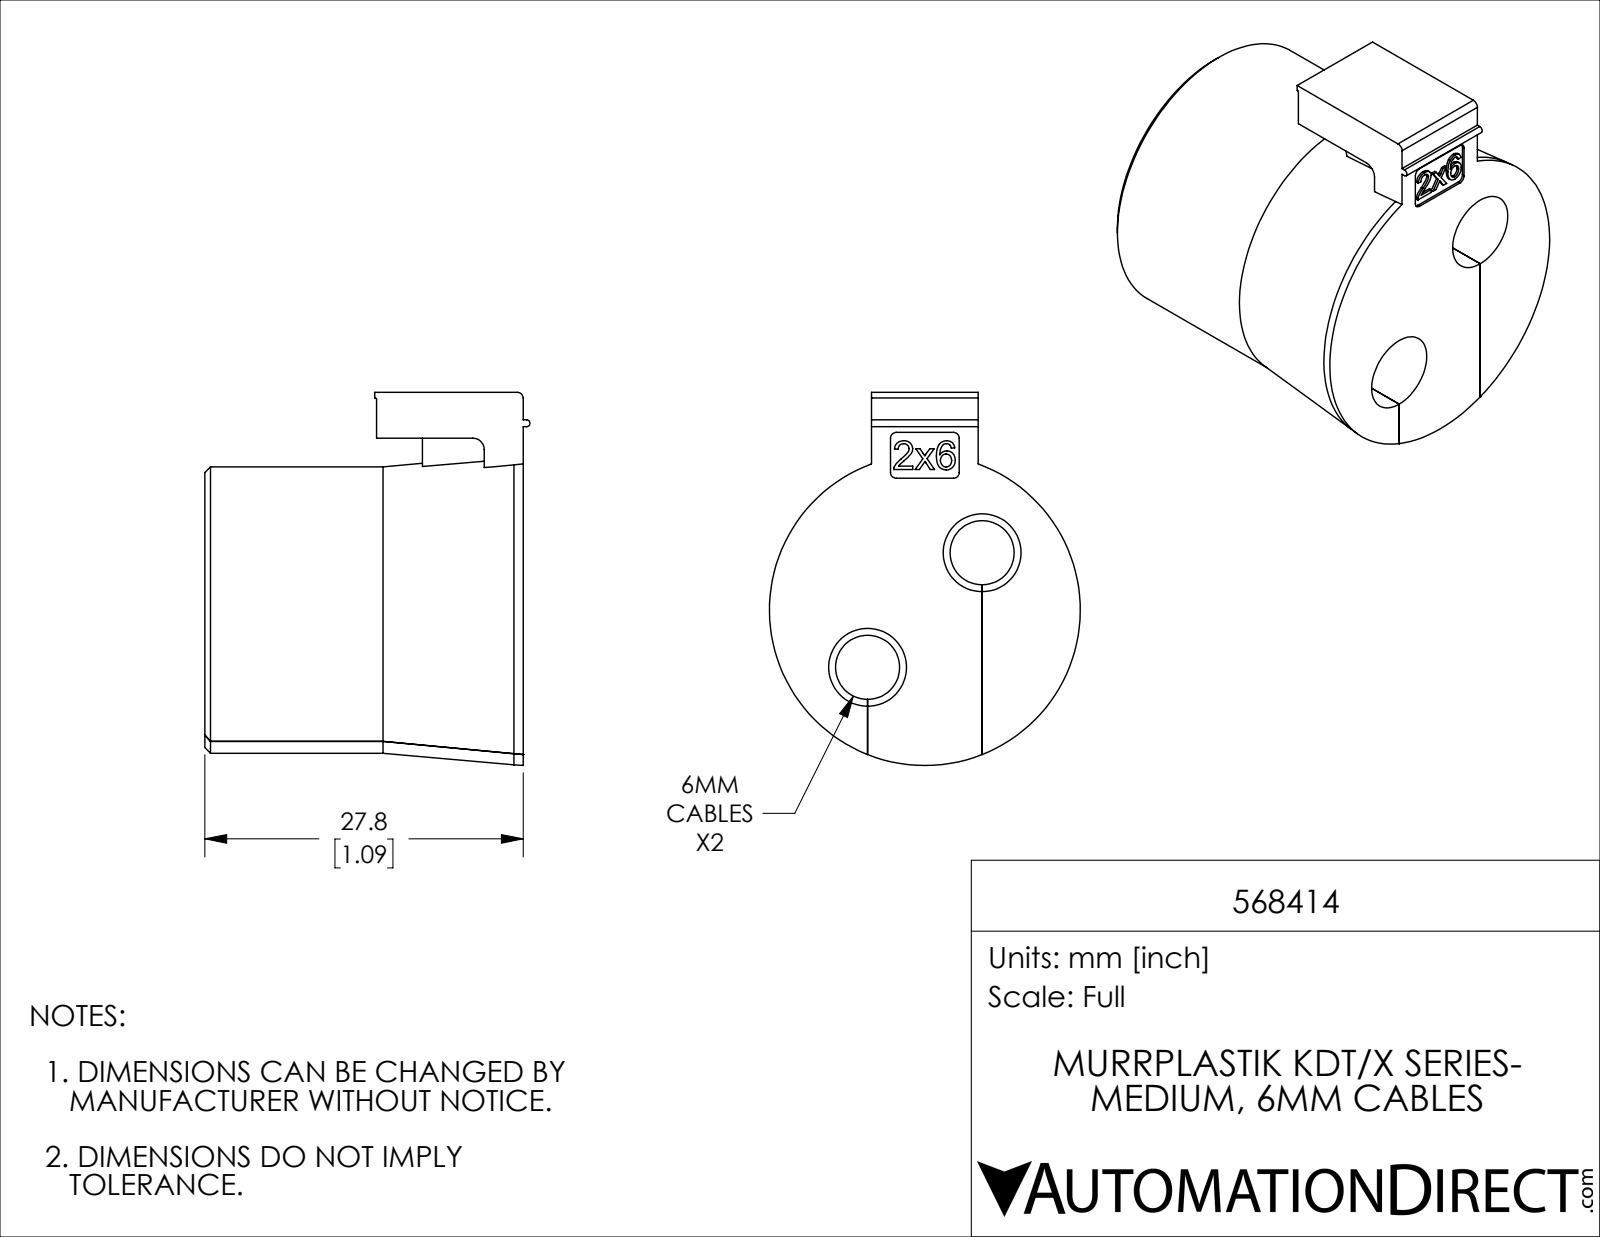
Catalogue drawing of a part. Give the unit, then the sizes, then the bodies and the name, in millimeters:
Units: millimetres
Overall size (bounding box): 32.6 × 28.4 × 27.2
Round holes (diameter × count): ⌀5.6 ×2, ⌀6.8 ×2
Round bosses / shafts (diameter × count): ⌀25 ×1
Partial cylindrical surfaces — rounded edges, fillets, slot ends (radius × count): R0.5 ×5, R0.1 ×1, R0.3 ×1, R1 ×1
Main face-to-face distances: 27.8, 10, 10, 0.4, 9.7, 4, 0.3, 9.3, 9.7, 12.8
Hole centre spacings: 14.1
Volume: 12 700 mm³ · Surface area: 5 648 mm²
Bodies: 1 solid, 130 faces (48 planar, 32 cylindrical, 50 other)
Part name (STEP PRODUCT): 568414
STEP written by: SolidWorks 2019 (CONFIG_CONTROL_DESIGN)
